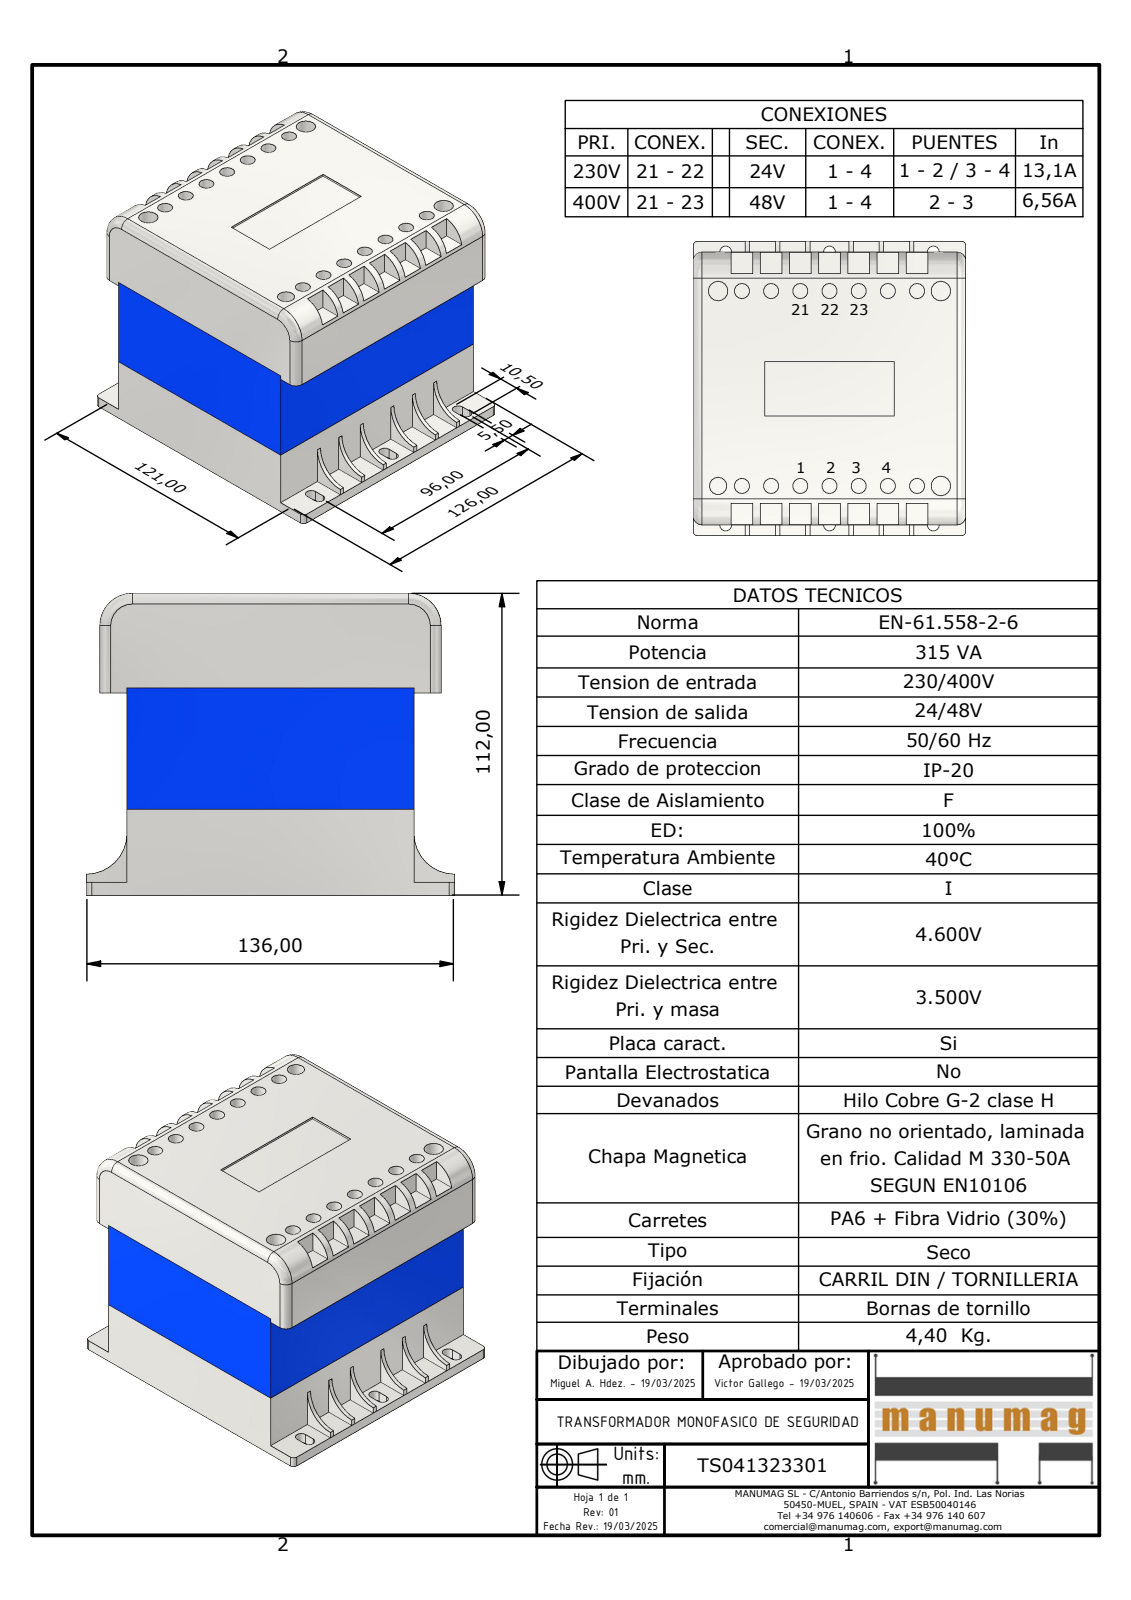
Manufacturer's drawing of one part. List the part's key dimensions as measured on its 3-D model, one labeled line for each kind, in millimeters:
Part name (STEP PRODUCT): TS041323301; INFERIOR EI120; CENTRAL EI120-40; SUPERIOR EI120
STEP written by: Autodesk Inventor 2023 (AUTOMOTIVE_DESIGN)
Units: millimetres
Bodies: 15 solids, 244 faces (186 planar, 54 cylindrical, 4 other)
Overall size (bounding box): 136 × 126 × 109
Volume: 650 729 mm³ · Surface area: 160 492 mm²
Round holes (diameter × count): ⌀7 ×14, ⌀9 ×3, ⌀8 ×1
Partial cylindrical surfaces — rounded edges, fillets, slot ends (radius × count): R2.75 ×12, R4 ×6, R2 ×4, R12 ×2, R15 ×2
Main face-to-face distances: 1, 104, 5, 105, 126, 74, 125, 69, 106, 109
Hole centre spacings: 13.5, 91.01, 27, 93.96, 90, 40.5, 98.69, 54
